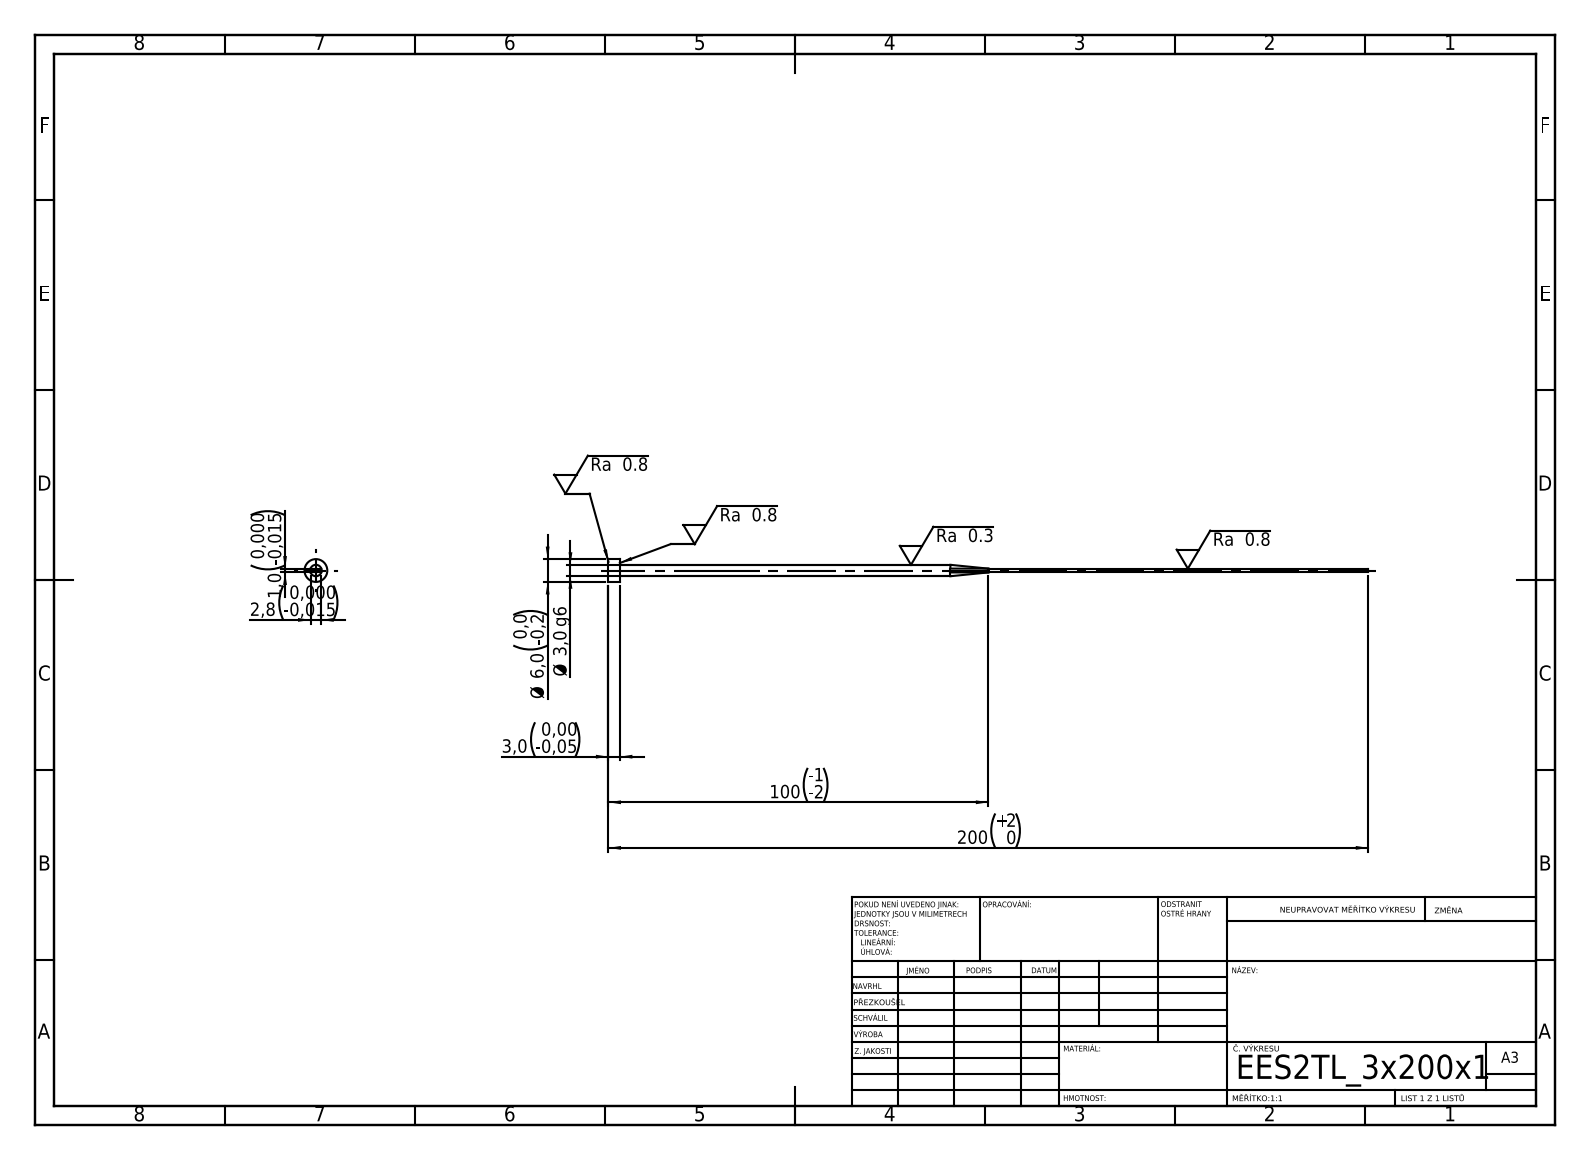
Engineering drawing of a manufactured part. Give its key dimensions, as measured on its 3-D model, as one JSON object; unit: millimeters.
{"step_written_by": "SolidWorks 2019 (CONFIG_CONTROL_DESIGN)", "units": "millimeters", "bodies": {"solids": 1, "faces": 15, "planar": 7, "cylindrical": 4, "other": 4}, "overall_size": [200, 6, 6], "volume_mm3": 1028, "surface_area_mm2": 1771, "round_bosses_or_shafts": [[6, 1], [3, 1]], "face_to_face_distances": [1, 2.8, 3, 200, 197]}
